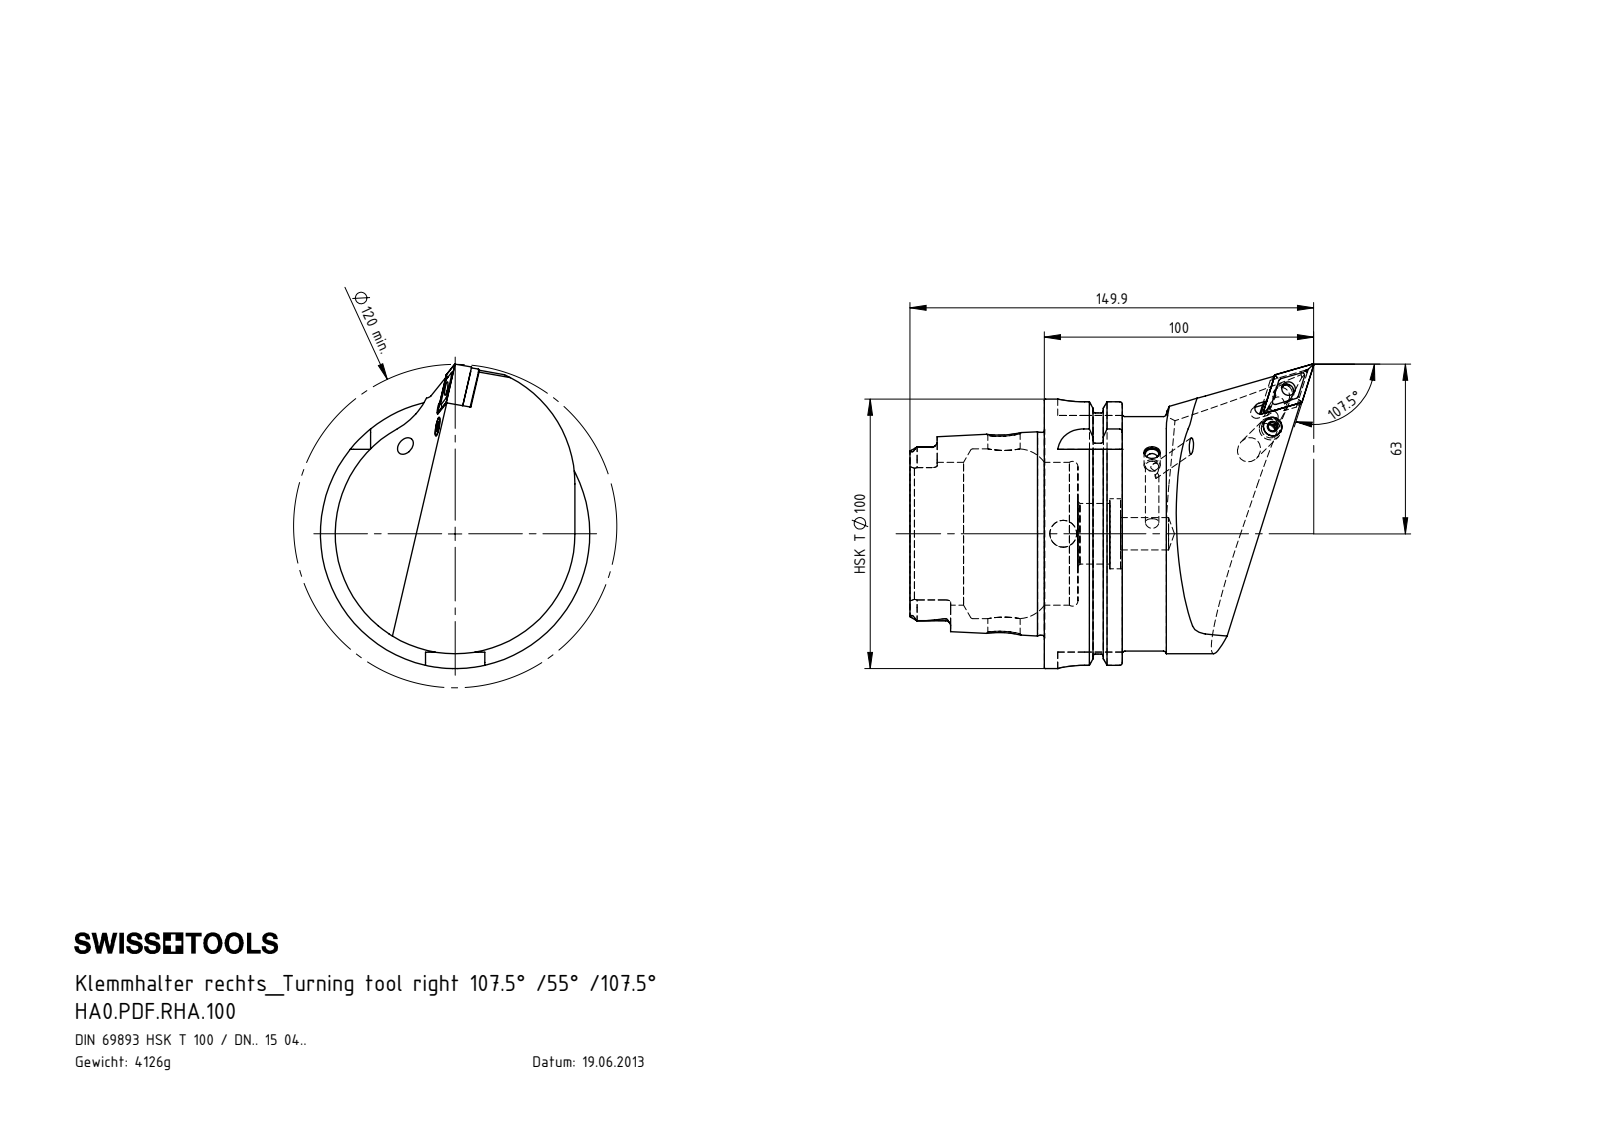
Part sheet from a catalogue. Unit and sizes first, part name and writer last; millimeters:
Units: millimetres
Overall size (bounding box): 149.9 × 113 × 100
Round holes (diameter × count): ⌀5 ×3, ⌀12 ×2, ⌀5.16 ×1, ⌀6 ×1, ⌀6.4 ×1, ⌀7 ×1, ⌀8.4 ×1, ⌀10 ×1, ⌀22.5 ×1, ⌀26 ×1, ⌀53 ×1, ⌀63 ×1
Round bosses / shafts (diameter × count): ⌀100 ×1, ⌀91.95 ×1, ⌀87 ×1, ⌀75.26 ×1, ⌀8 ×1, ⌀7.9 ×1, ⌀6.4 ×1, ⌀6 ×1
Partial cylindrical surfaces — rounded edges, fillets, slot ends (radius × count): R1.9 ×6, R0.4 ×4, R1 ×4, R4.88 ×4, R10 ×4, R2.5 ×2, R44.5 ×2, R2.1 ×1
Main face-to-face distances: 12.45, 28.95, 16.5, 49.9, 62.35, 78.85, 87.8, 78.2, 28.3, 15.85
Hole centre spacings: 15.6
Volume: 526 485 mm³ · Surface area: 70 534 mm²
Bodies: 8 solids, 371 faces (113 planar, 103 cylindrical, 155 other)
Part name (STEP PRODUCT): HA0.PDF.RHA.100; DNMG150604; WDF-ER2.101.003_A; WCD-ER1.101.000 (+4 more)
STEP written by: SolidWorks 2012 (CONFIG_CONTROL_DESIGN)
